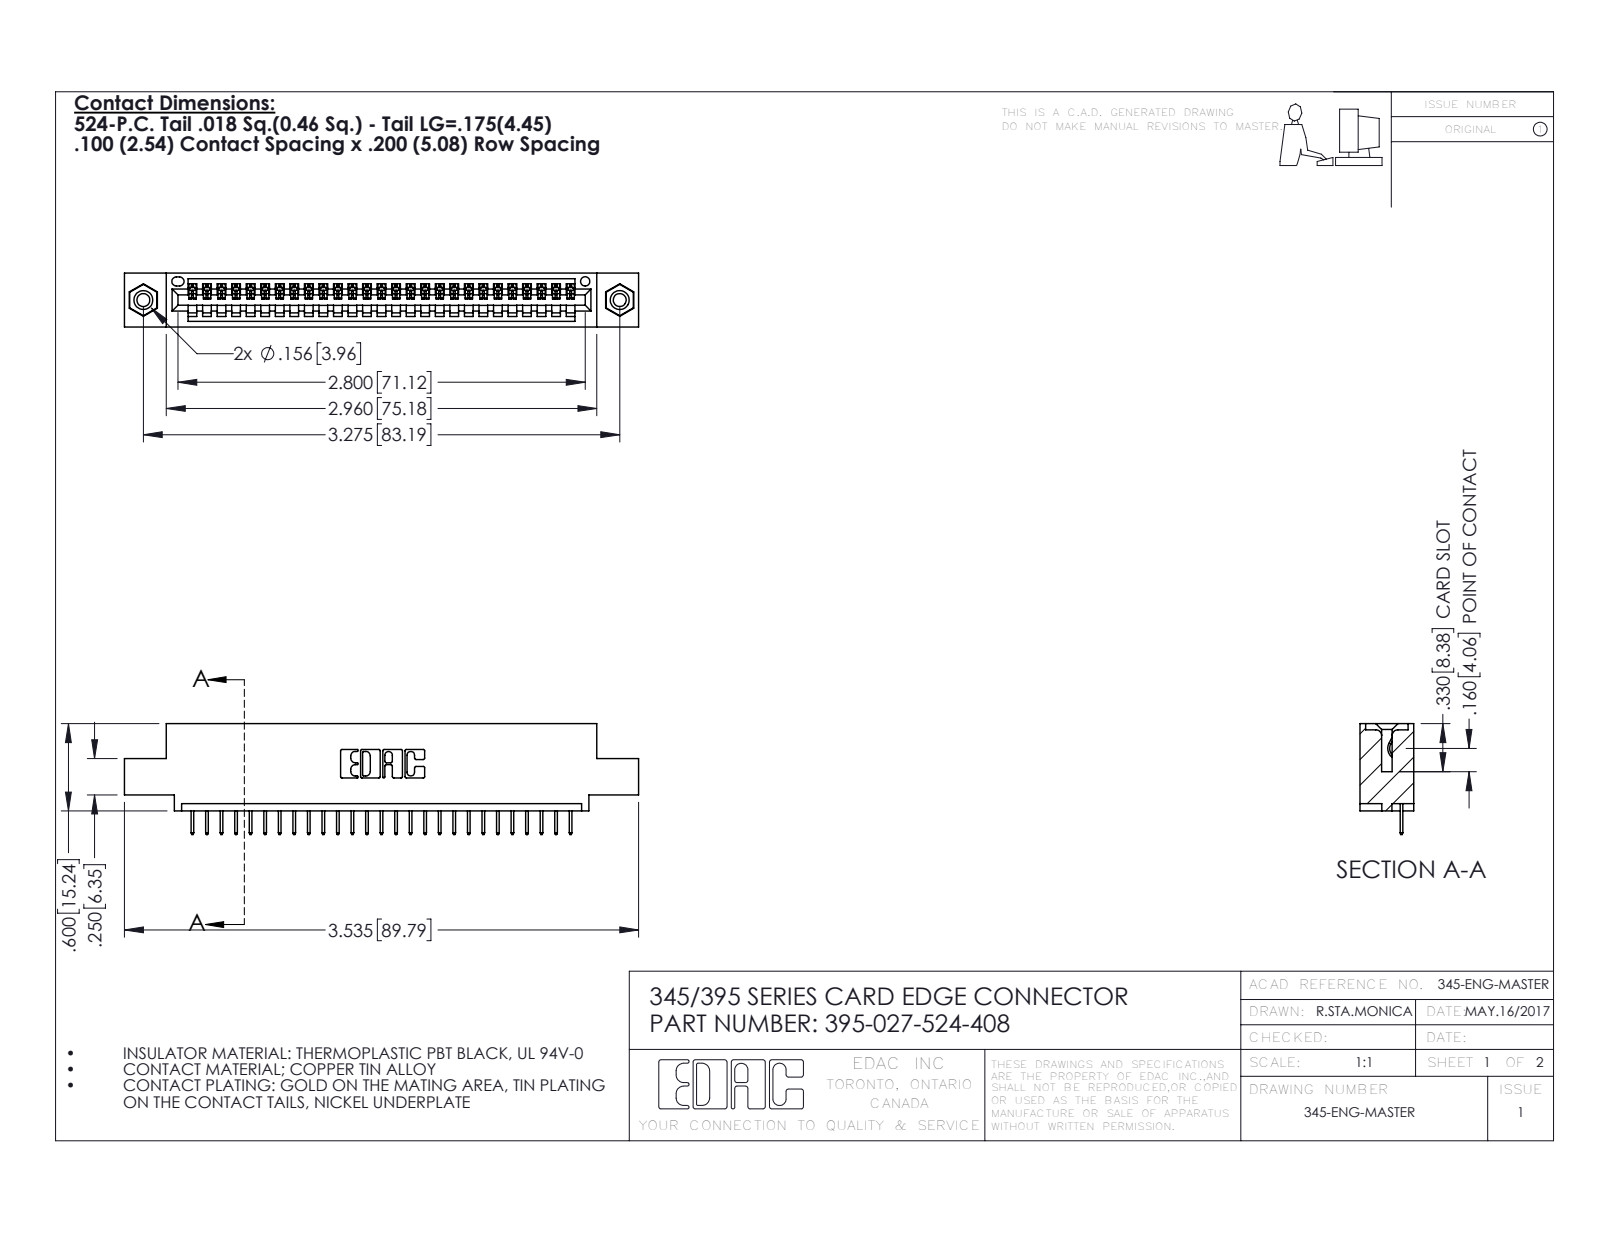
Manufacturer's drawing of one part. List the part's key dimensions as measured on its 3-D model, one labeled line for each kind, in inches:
Part name (STEP PRODUCT): 345-292-001_345-293-124; 395-027-524-408; 345 Part_0.110 Offset - 0.156 Dia-TI; 345-250-001_345-250-003-102
STEP written by: SolidWorks 2016 (CONFIG_CONTROL_DESIGN)
Units: inches
Bodies: 30 solids, 1864 faces (1358 planar, 490 cylindrical, 16 other)
Overall size (bounding box): 3.535 × 0.762 × 0.37
Volume: 0.502 in³ · Surface area: 16.24 in²
Round holes (diameter × count): ⌀0.089 ×2, ⌀0.125 ×2, ⌀0.156 ×2, ⌀0.064 ×1
Round bosses / shafts (diameter × count): ⌀0.155 ×2
Partial cylindrical surfaces — rounded edges, fillets, slot ends (radius × count): R0.006 ×54, R0.01 ×22, R0.007 ×6, R0.031 ×6, R0.026 ×3, R0.031 ×2, R0.04 ×2, R0.014 ×1
Main face-to-face distances: 0.072, 0.298, 0.37, 0.2, 0.098, 0.272, 0.025, 0.225, 0.072, 0.149
Hole centre spacings: 0.27, 3.04, 3.275
